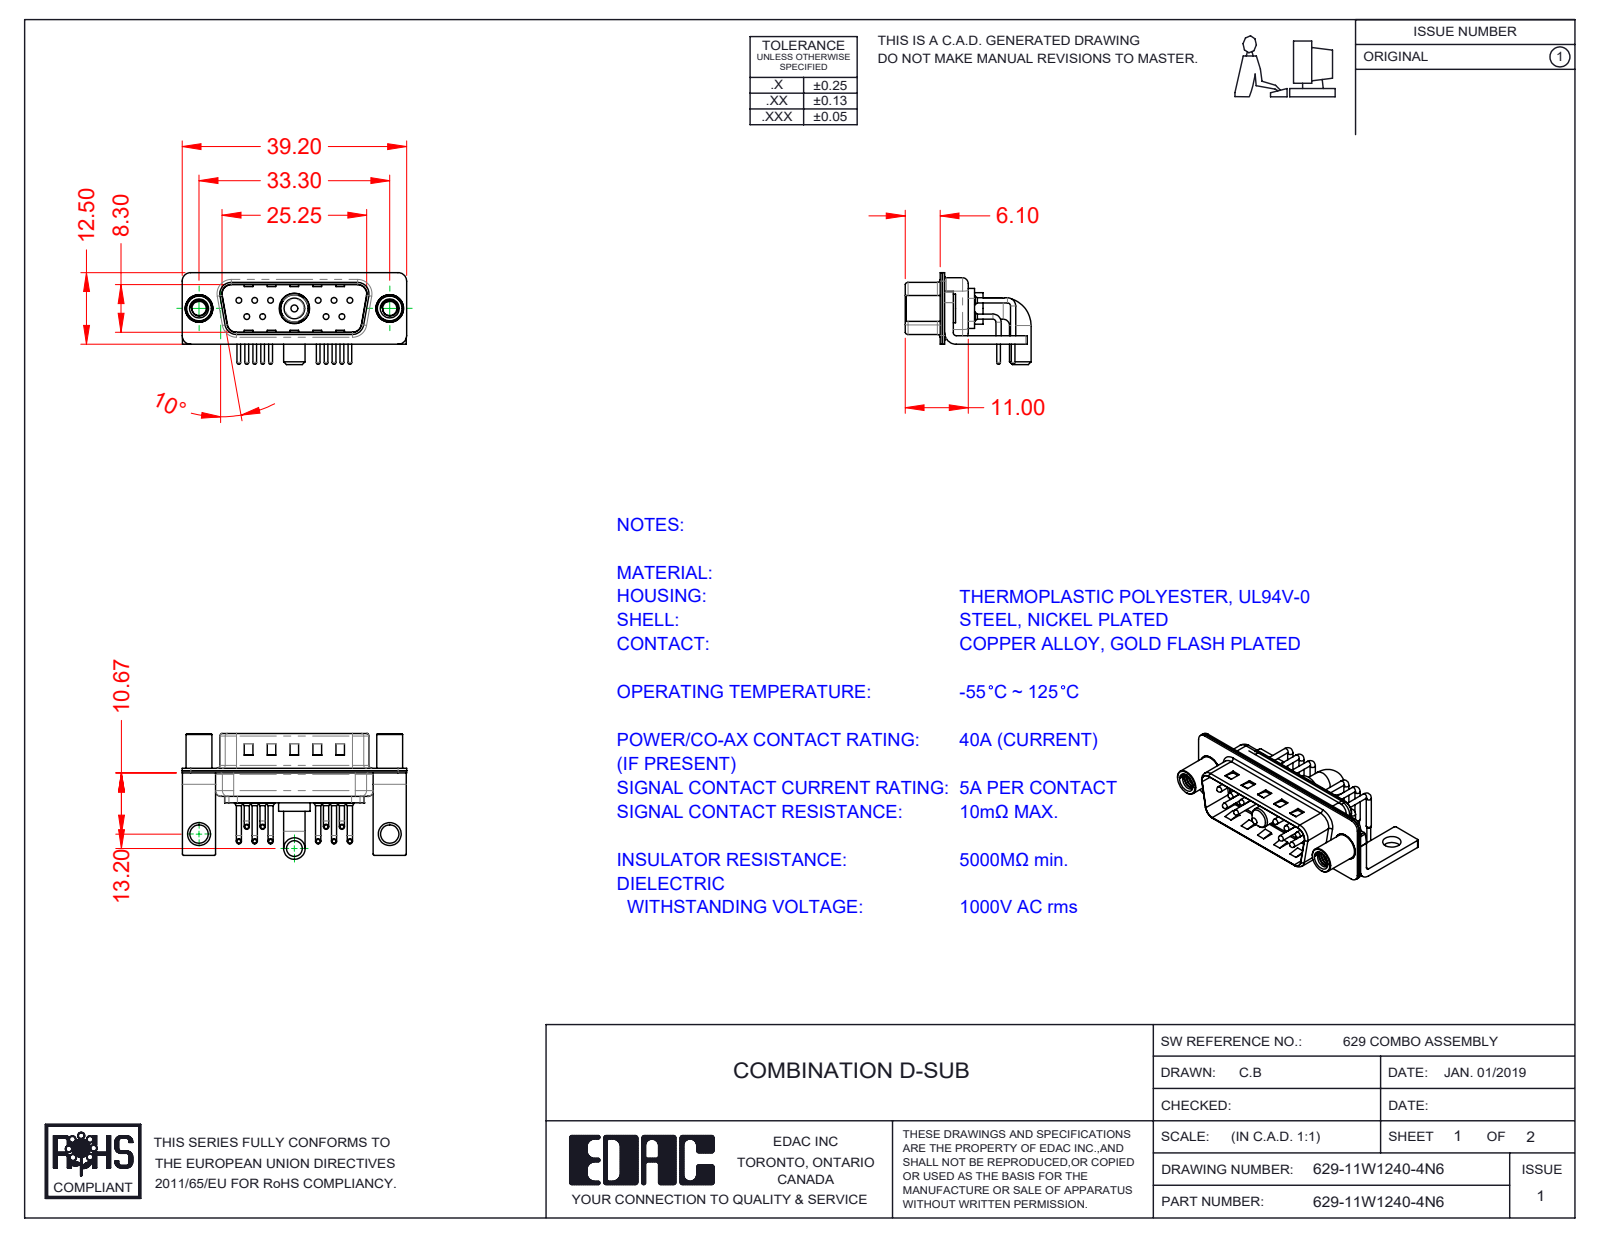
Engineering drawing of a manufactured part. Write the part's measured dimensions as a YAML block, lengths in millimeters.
part_name: "Power Pin_40A RA; 629Combo Shell Front_15 Contacts; 629Combo Stabilizer Bracket; 629Combo Housing_11W1 (+5 more)"
step_written_by: "SolidWorks 2020 (CONFIG_CONTROL_DESIGN)"
units: millimeters
bodies: {solids: 19, faces: 1594, planar: 820, cylindrical: 590, other: 184}
overall_size: [39.2, 21.98, 16.05]
volume: 2520
surface_area: 6202
round_holes:
  - {diameter: 0.75, count: 10}
  - {diameter: 1.6, count: 10}
  - {diameter: 2, count: 10}
  - {diameter: 2.5, count: 2}
  - {diameter: 3.2, count: 2}
  - {diameter: 4, count: 2}
  - {diameter: 4.8, count: 2}
  - {diameter: 4.85, count: 1}
  - {diameter: 5.3, count: 1}
round_bosses_or_shafts:
  - {diameter: 0.9, count: 20}
  - {diameter: 1.5, count: 10}
  - {diameter: 1, count: 10}
  - {diameter: 0.65, count: 10}
  - {diameter: 5, count: 2}
  - {diameter: 4.9, count: 2}
  - {diameter: 4.5, count: 2}
  - {diameter: 3.75, count: 2}
partial_cylinders:
  - {radius: 0.25, count: 16}
  - {radius: 1.5, count: 16}
  - {radius: 2, count: 13}
  - {radius: 1.01, count: 10}
  - {radius: 0.5, count: 9}
  - {radius: 1.6, count: 8}
  - {radius: 1, count: 7}
  - {radius: 0.6, count: 4}
face_to_face_distances: [0.4, 0.8, 1.5, 9.5, 9.1, 8.7, 9.9, 0.6, 1.9, 2.1]
hole_center_spacings: [3.16, 2.77, 13.85, 11.08, 16.62, 5.03, 5.04, 5.54]
